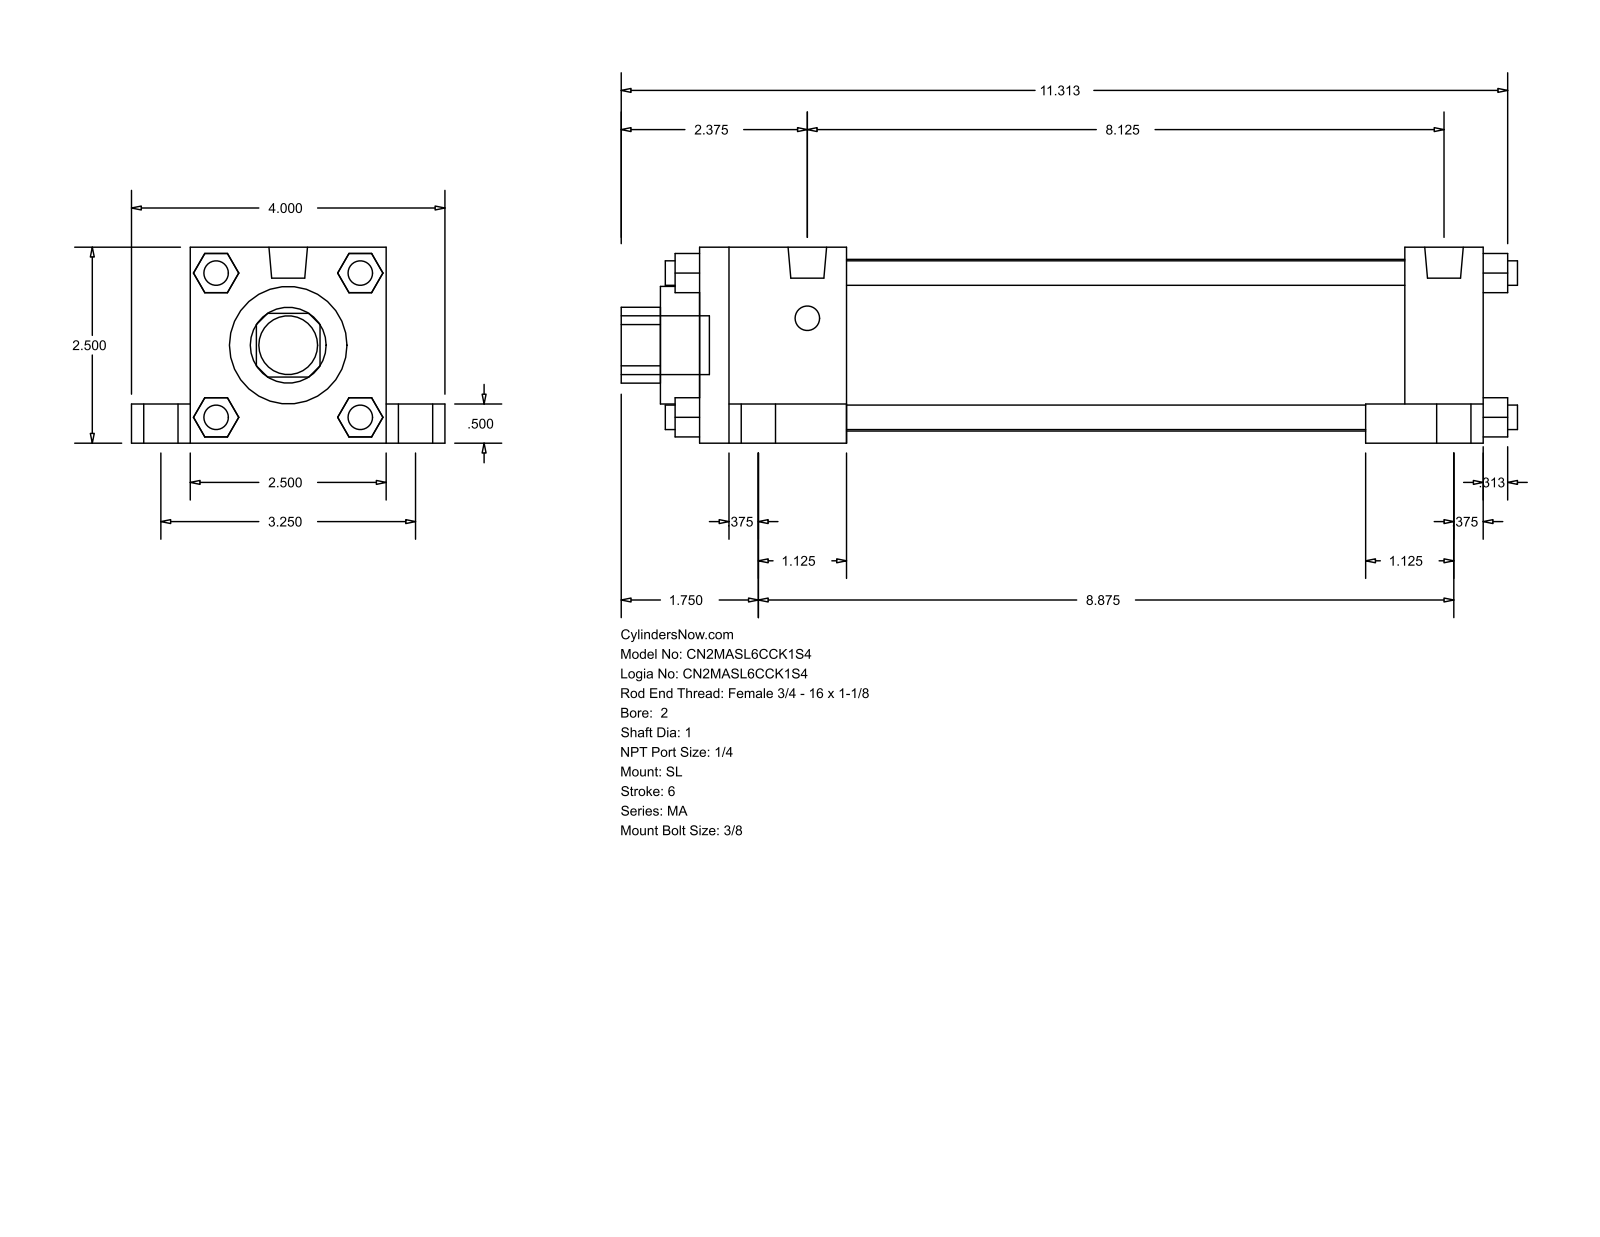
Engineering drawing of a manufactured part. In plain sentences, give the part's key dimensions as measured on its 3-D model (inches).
The part is named "MA_SL__0200_1". Its 3-D file was written by "GSSL Pune (CONFIG_CONTROL_DESIGN)". It is 0 solids with 148 faces: 112 planar, 36 cylindrical and 0 other. Overall it measures 11.437 by 4 by 2.5 inches. Round holes: 1 of diameter 1, 1 of diameter 1.5, 1 of diameter 2.19. Round bosses or shafts: 8 of diameter 0.313, 4 of diameter 0.687, 4 of diameter 0.437, 2 of diameter 0.492, 1 of diameter 0.75. Partial cylindrical surfaces (rounded edges, fillets, slot ends): 1 of radius 0.484. The main face-to-face distances are 2.5, 0.5, 10, 0.75, 3.25, 1, 2, 1.875, 8.125, 9.
